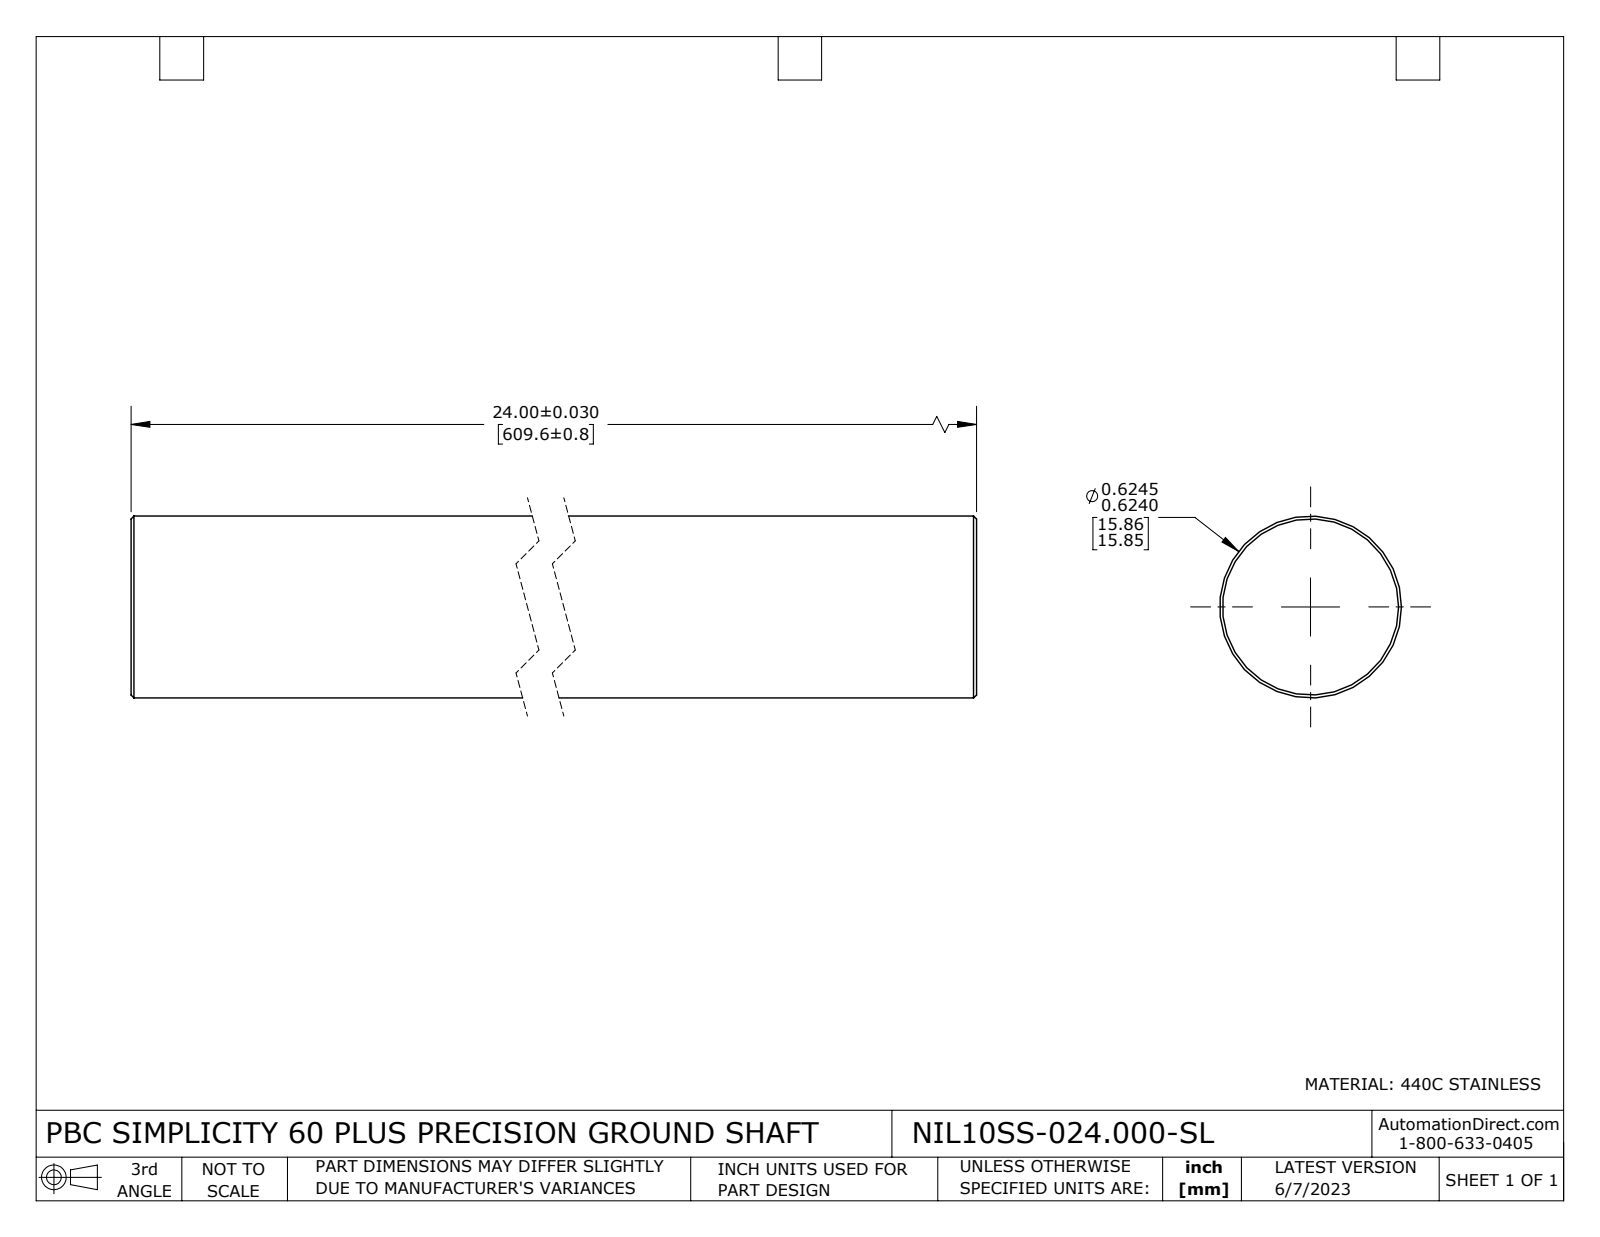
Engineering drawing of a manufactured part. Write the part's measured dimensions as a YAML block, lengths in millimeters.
part_name: "NIL10SS-024.000-SL"
step_written_by: "SolidWorks 2021 (CONFIG_CONTROL_DESIGN)"
units: millimeters
bodies: {solids: 1, faces: 8, planar: 2, cylindrical: 2, other: 4}
overall_size: [609.6, 15.9, 15.9]
volume: 120700
surface_area: 30780
round_bosses_or_shafts:
  - {diameter: 15.9, count: 1}
face_to_face_distances: [609.6]
